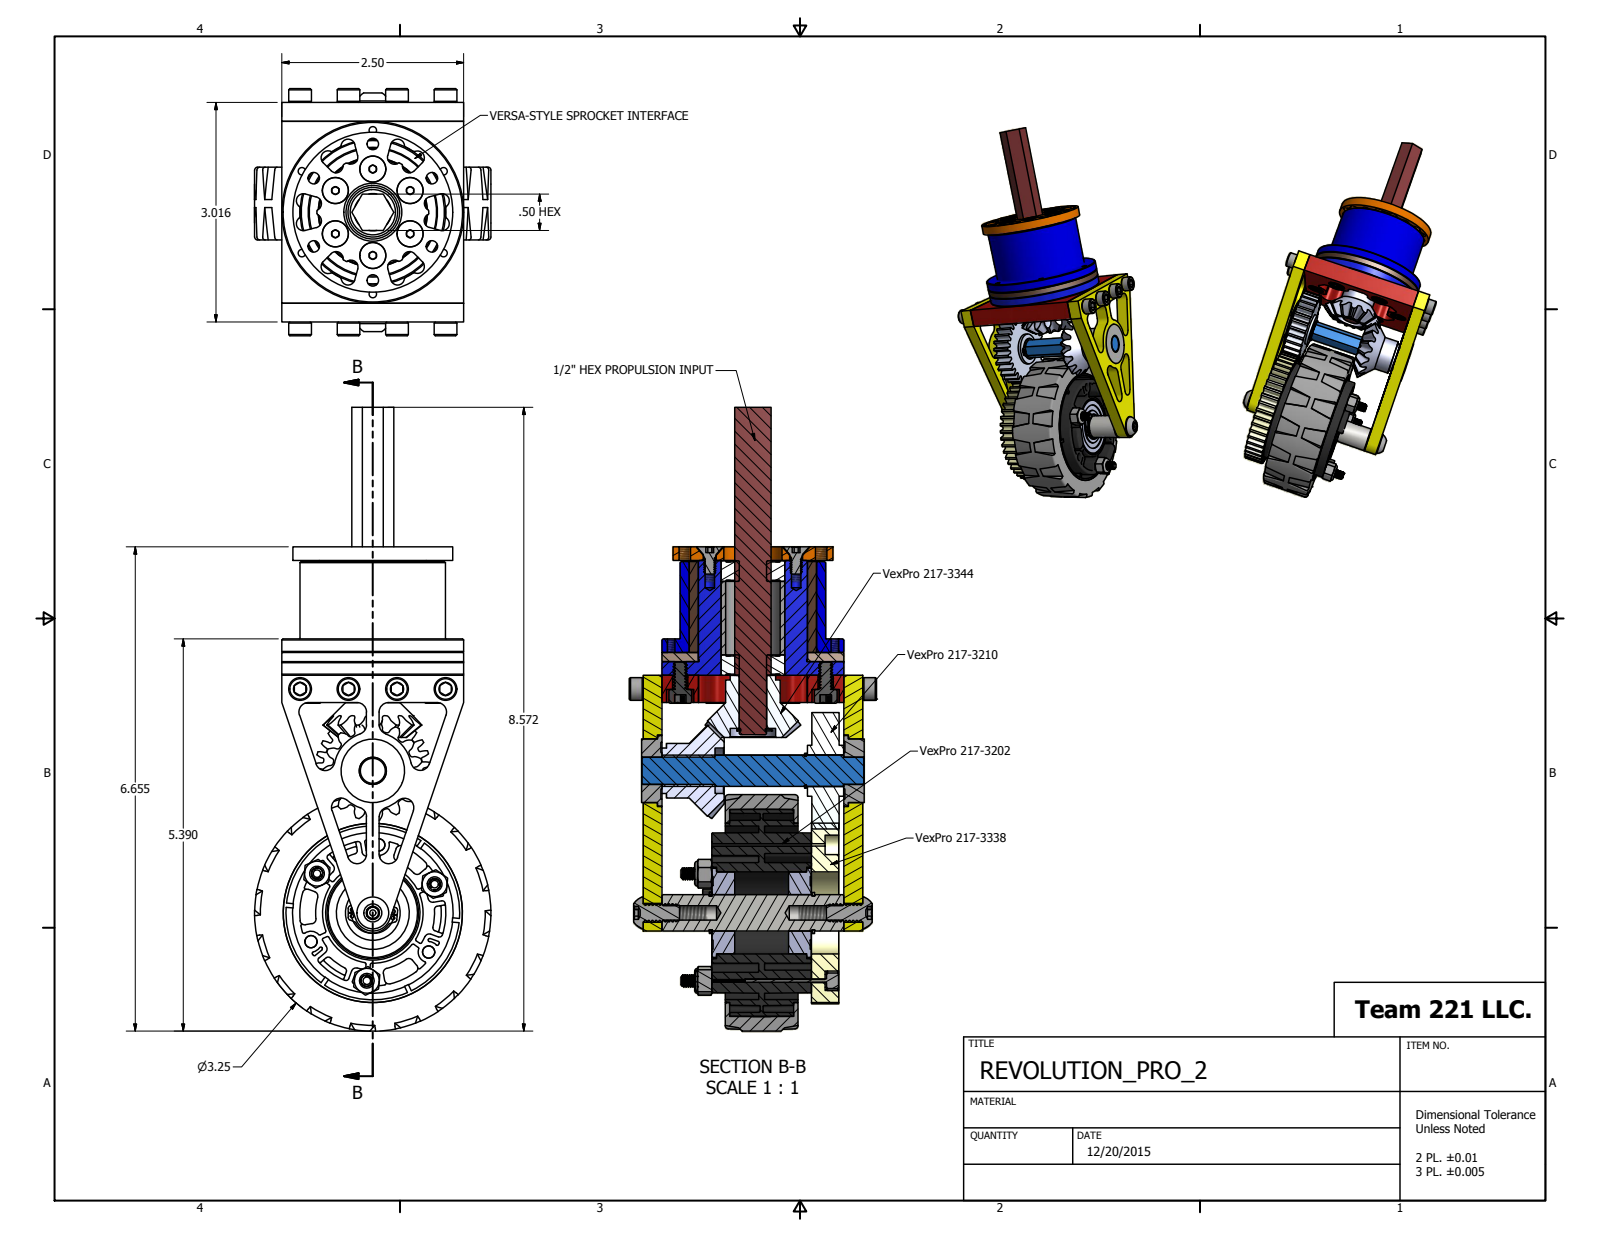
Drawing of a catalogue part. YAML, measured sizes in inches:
part_name: "RP-003-A; 5906K526_thrust_bushing; 1.75id_bushing_short; RP-005-A (+8 more)"
step_written_by: "Autodesk Inventor 2014 (AUTOMOTIVE_DESIGN)"
units: inches
bodies: {solids: 60, faces: 3690, planar: 841, cylindrical: 1115, other: 1734}
overall_size: [8.572, 3.396, 3.25]
volume: 19.37
surface_area: 328.8
round_holes:
  - {diameter: 0.14, count: 18}
  - {diameter: 0.156, count: 16}
  - {diameter: 0.079, count: 12}
  - {diameter: 0.047, count: 6}
  - {diameter: 0.104, count: 6}
  - {diameter: 0.13, count: 6}
  - {diameter: 0.169, count: 6}
  - {diameter: 0.17, count: 6}
  - {diameter: 0.177, count: 6}
  - {diameter: 0.21, count: 6}
  - {diameter: 0.315, count: 6}
  - {diameter: 0.375, count: 6}
round_bosses_or_shafts:
  - {diameter: 0.212, count: 18}
  - {diameter: 0.312, count: 10}
  - {diameter: 0.19, count: 10}
  - {diameter: 0.123, count: 9}
  - {diameter: 0.359, count: 6}
  - {diameter: 0.164, count: 6}
  - {diameter: 0.136, count: 6}
  - {diameter: 0.149, count: 4}
partial_cylinders:
  - {radius: 0.012, count: 178}
  - {radius: 0.02, count: 88}
  - {radius: 0.039, count: 54}
  - {radius: 0.13, count: 38}
  - {radius: 0.063, count: 36}
  - {radius: 0.02, count: 24}
  - {radius: 0.095, count: 24}
  - {radius: 0.035, count: 12}
face_to_face_distances: [0.187, 0.375, 0.059, 0.258, 2.758, 0.125, 0.312, 1.578, 2.5, 0.941]
hole_center_spacings: [0.937, 1.624, 1.326, 1.875, 0.594, 0.871, 0.975, 1]
